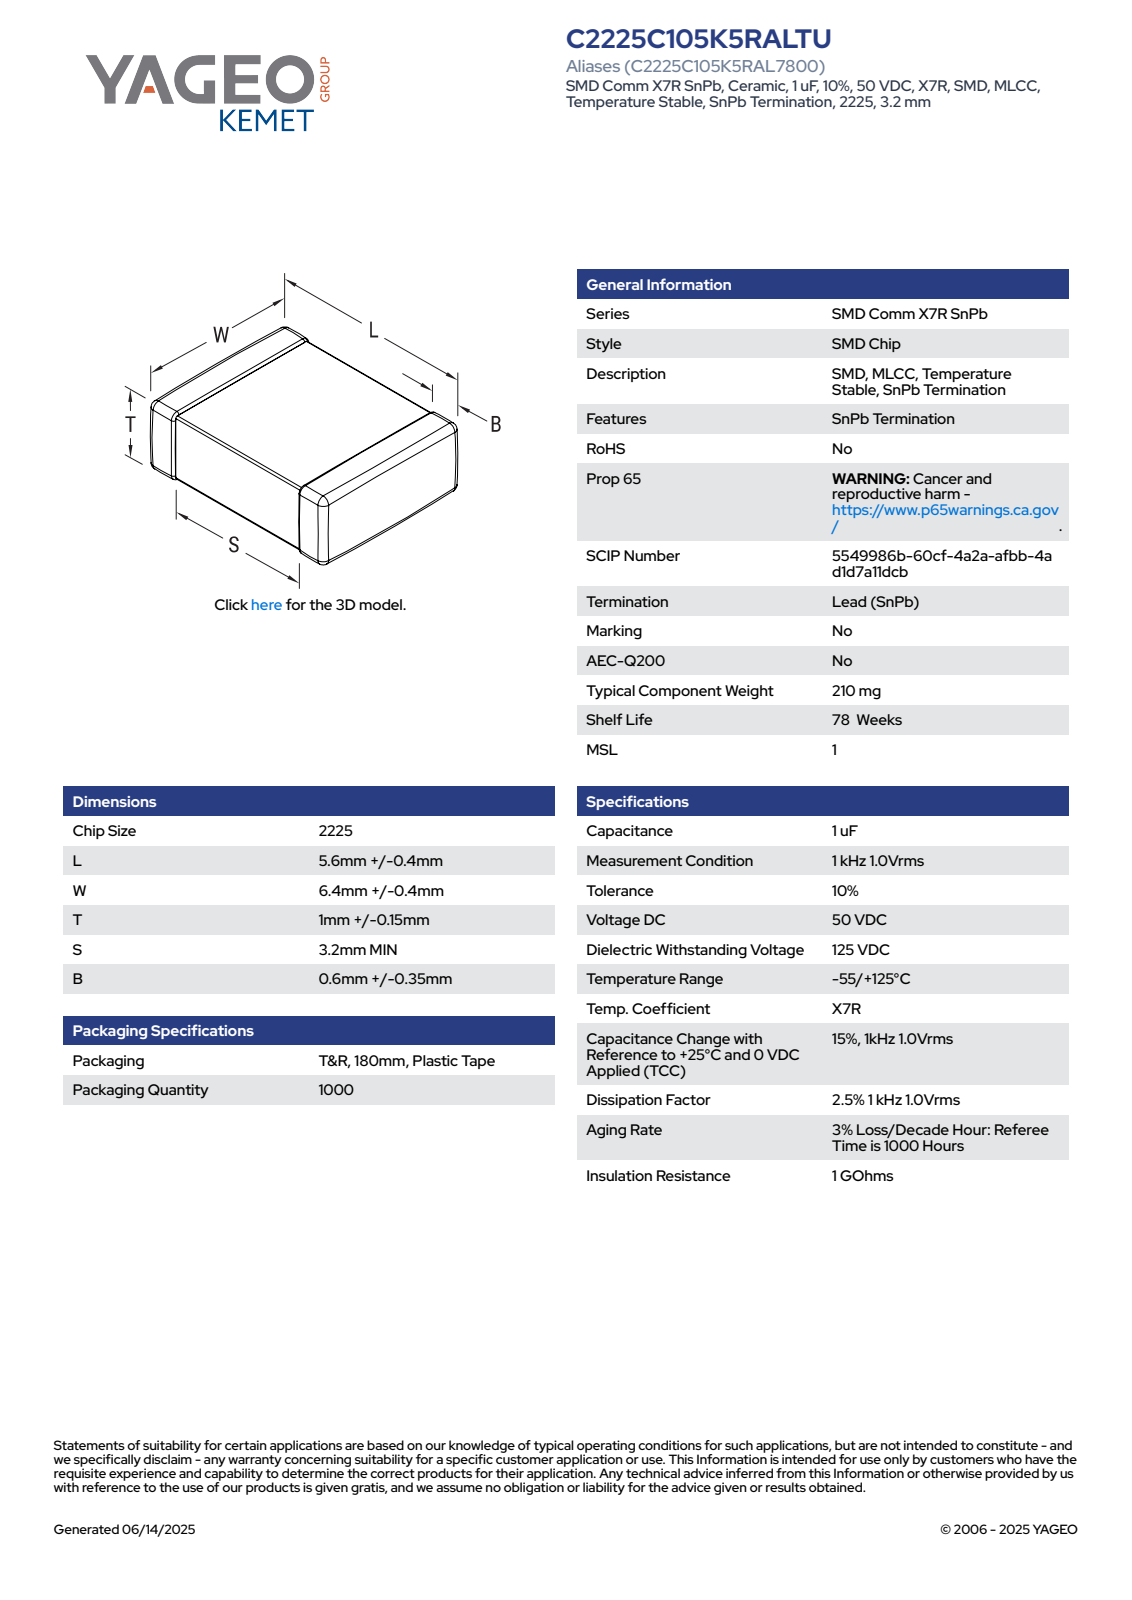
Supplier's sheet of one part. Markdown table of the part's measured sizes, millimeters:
| quantity | value |
| --- | --- |
| part name | CCS_CCSTDNOS_2225_L6W6.8T1.15B0.95 |
| STEP written by | SolidWorks 2014 (AUTOMOTIVE_DESIGN) |
| units | millimeters |
| bodies | 4 solids, 125 faces (71 planar, 38 cylindrical, 16 other) |
| overall size | 6.8 × 6 × 1.15 |
| volume | 38 mm³ |
| surface area | 107 mm² |
| partial cylindrical surfaces (radius × count) | 0.14 × 24 |
| main face-to-face distances | 0.87, 1.01, 1.15, 6, 6.52, 6.66, 6.8, 3.33, 0.43, 3.47 |
